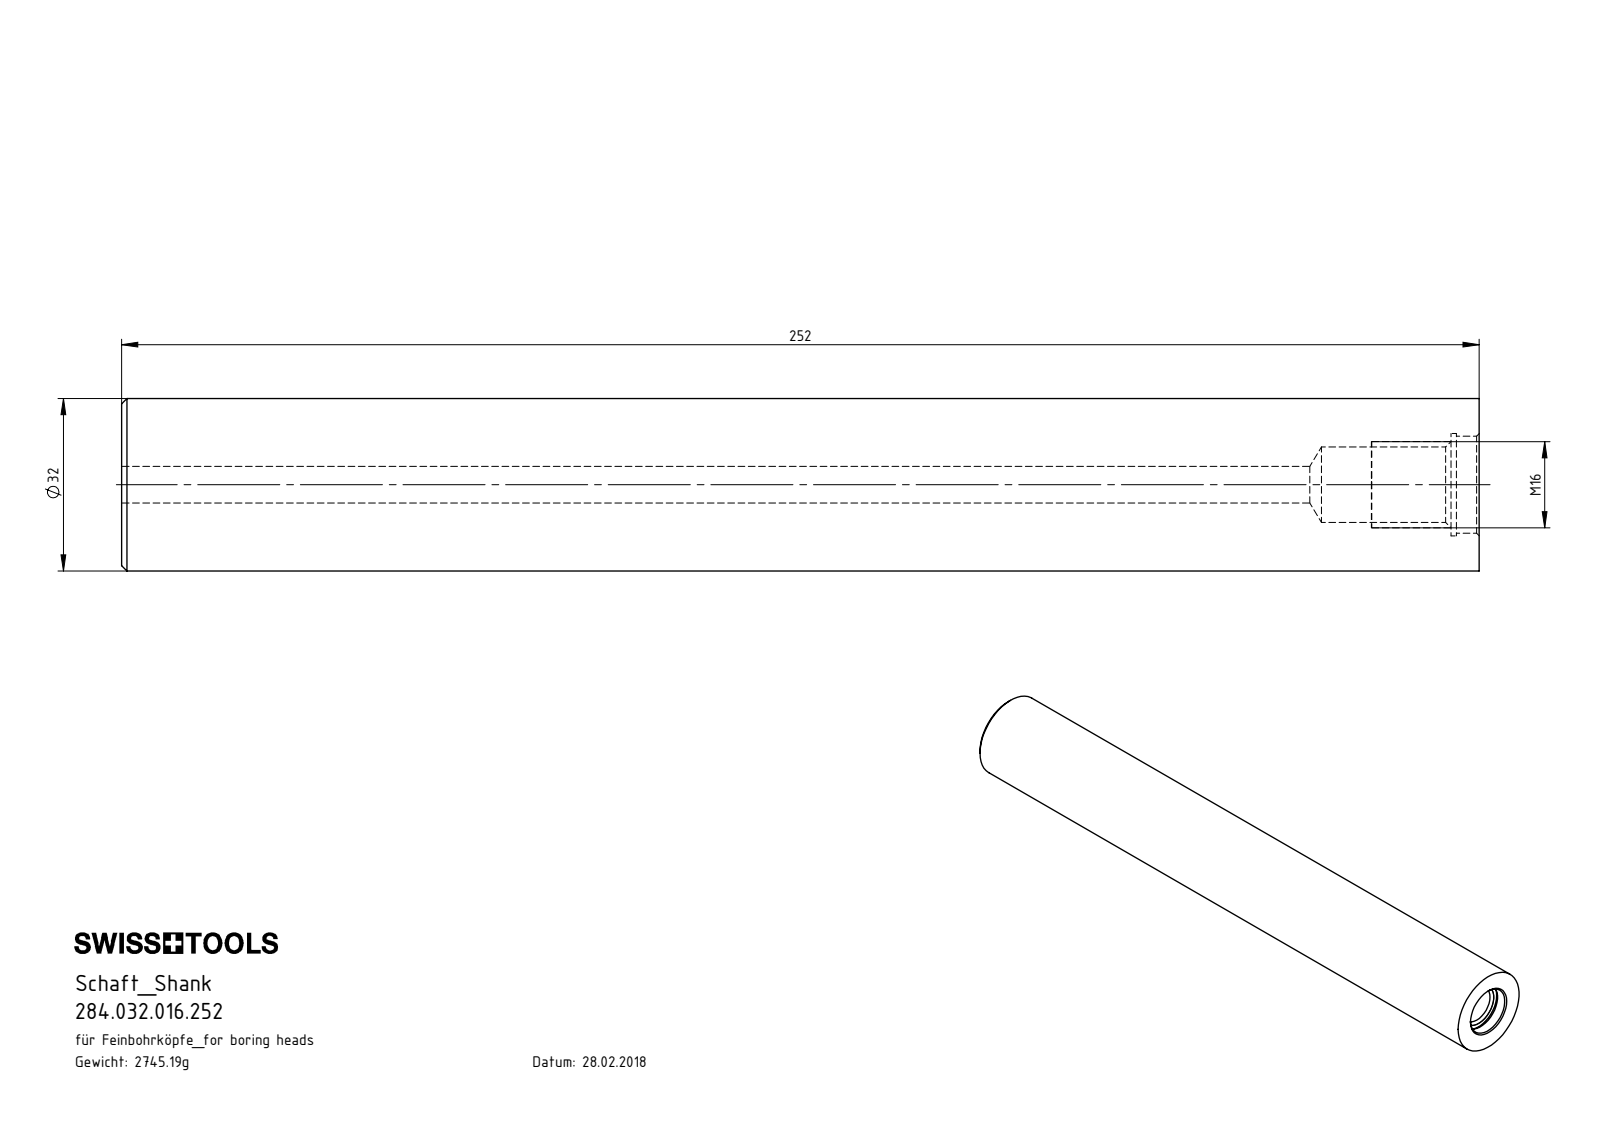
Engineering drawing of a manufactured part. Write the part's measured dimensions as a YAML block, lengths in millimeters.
part_name: "284.032.016.252"
step_written_by: "SolidWorks 2017 (CONFIG_CONTROL_DESIGN)"
units: millimeters
bodies: {solids: 1, faces: 22, planar: 4, cylindrical: 10, other: 8}
overall_size: [252, 32, 32]
volume: 189323
surface_area: 32916
round_holes:
  - {diameter: 6.8, count: 1}
  - {diameter: 14, count: 1}
  - {diameter: 18, count: 1}
  - {diameter: 19, count: 1}
round_bosses_or_shafts:
  - {diameter: 32, count: 1}
face_to_face_distances: [252, 246.75, 5.25, 247.75, 1, 4.25]
